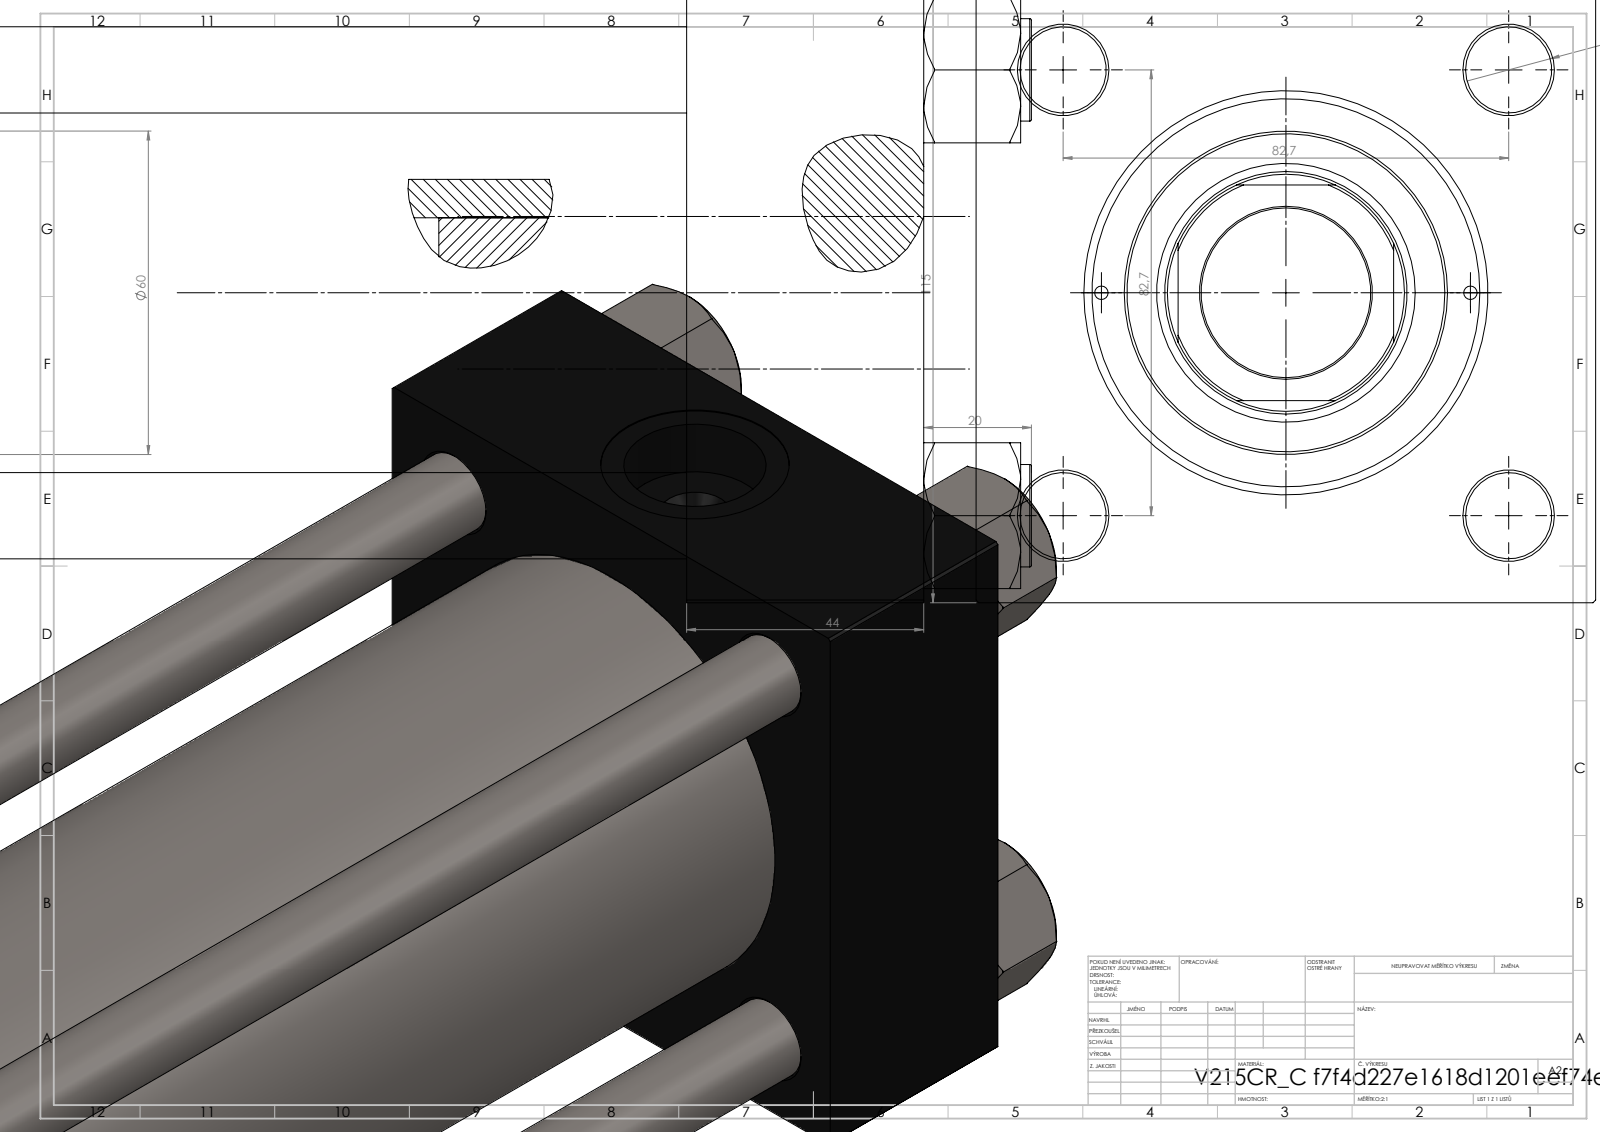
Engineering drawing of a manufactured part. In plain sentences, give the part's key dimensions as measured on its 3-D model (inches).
The part is named "V215CR_C_Body; NUT_M5_C; V215CR_VCP_C; V215CR_C_TYCINKA (+1 more)". Its 3-D file was written by "SolidWorks 2019 (CONFIG_CONTROL_DESIGN)". It is 11 solids with 1203 faces: 576 planar, 91 cylindrical and 536 other. Overall it measures 22.047 by 4.528 by 4.528 inches. Its volume is 175 cubic inches and its surface area 866.5 square inches. Round holes: 4 of diameter 0.63, 2 of diameter 0.098, 2 of diameter 0.276, 2 of diameter 1.041, 2 of diameter 1.378, 1 of diameter 1.24, 1 of diameter 1.772, 1 of diameter 1.89, 1 of diameter 2.402, 1 of diameter 2.835, 1 of diameter 3.15. Round bosses or shafts: 4 of diameter 0.748, 1 of diameter 3.386, 1 of diameter 2.362. Partial cylindrical surfaces (rounded edges, fillets, slot ends): 1 of radius 0.866. The main face-to-face distances are 4.528, 1.732, 20.039, 18.307, 17.323, 15.591, 2.717, 18.909, 17.177, 1.587. The hole center spacings are 1.652, 2.302, 3.256, 3.393, 1.348, 4.605, 2.697, 17.362.
